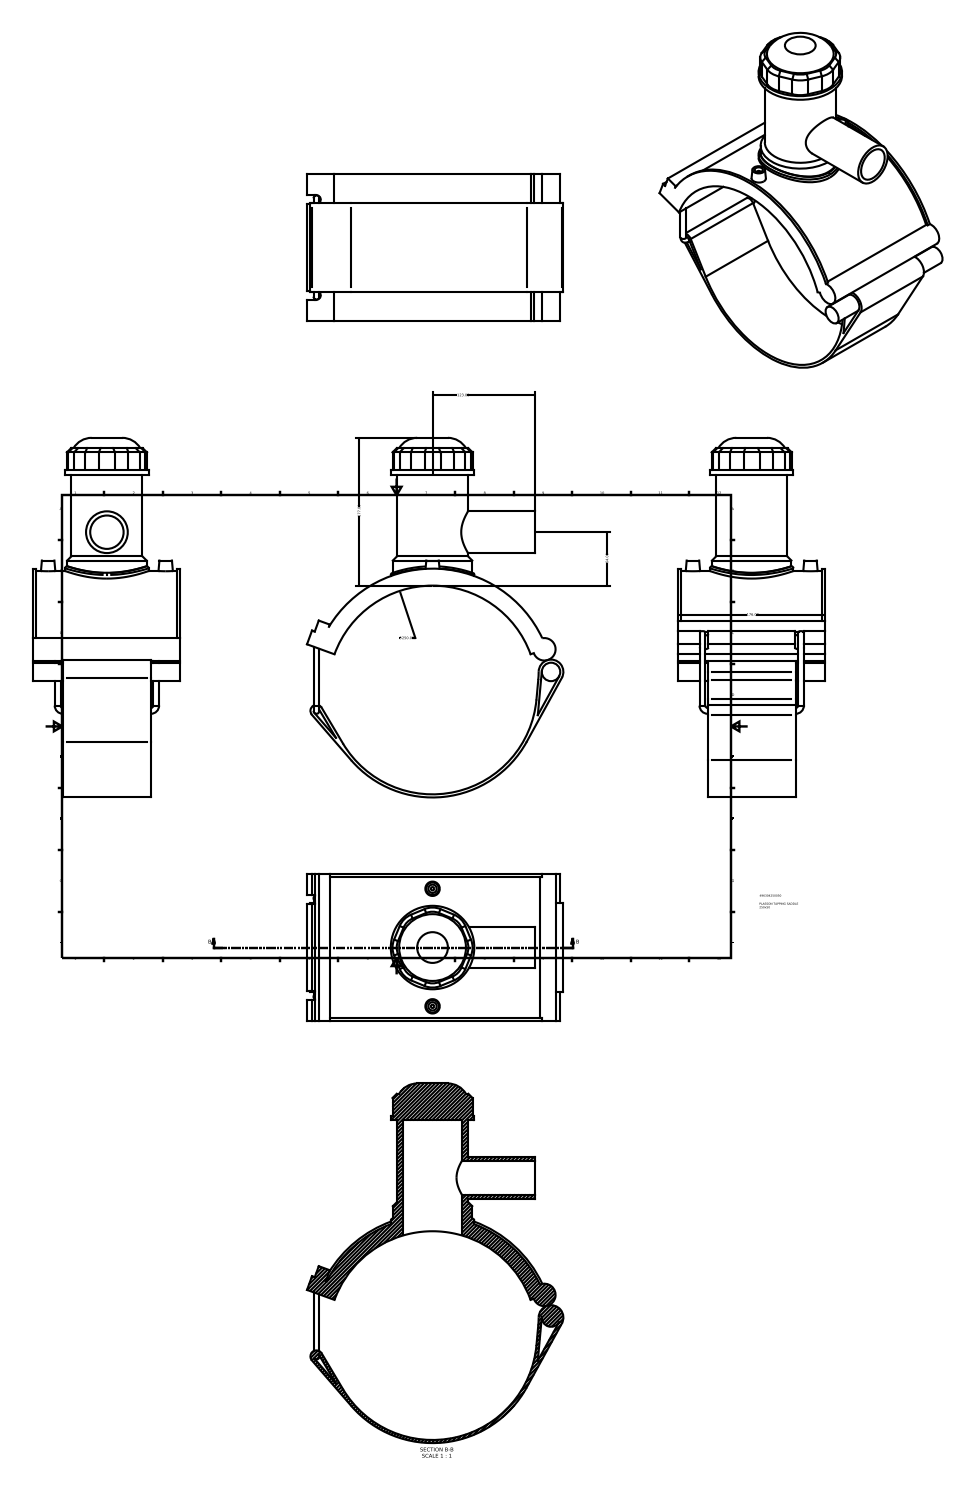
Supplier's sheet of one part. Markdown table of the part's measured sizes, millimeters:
| quantity | value |
| --- | --- |
| part name | 496304250050 |
| STEP written by | Autodesk Inventor 2015 (AUTOMOTIVE_DESIGN) |
| units | millimeters |
| bodies | 1 solid, 121 faces (68 planar, 38 cylindrical, 15 other) |
| overall size | 430.75 × 307.08 × 176 |
| volume | 1 981 000 mm³ |
| surface area | 387 411 mm² |
| round holes (diameter × count) | 10 × 2, 40 × 1, 70 × 1 |
| round bosses / shafts (diameter × count) | 7 × 2, 4 × 2, 100 × 1, 95 × 1, 85 × 1, 50 × 1, 22.12 × 1 |
| partial cylindrical surfaces (radius × count) | 25 × 8, 5.25 × 2, 125 × 2, 3.5 × 1, 7.25 × 1, 13.46 × 1, 14.81 × 1, 128.75 × 1 |
| main face-to-face distances | 3.75, 176, 3.78, 35.2, 140.8, 17.5, 14, 3.34, 31.51, 3.5 |
| hole center spacings | 70.4, 140.8 |
